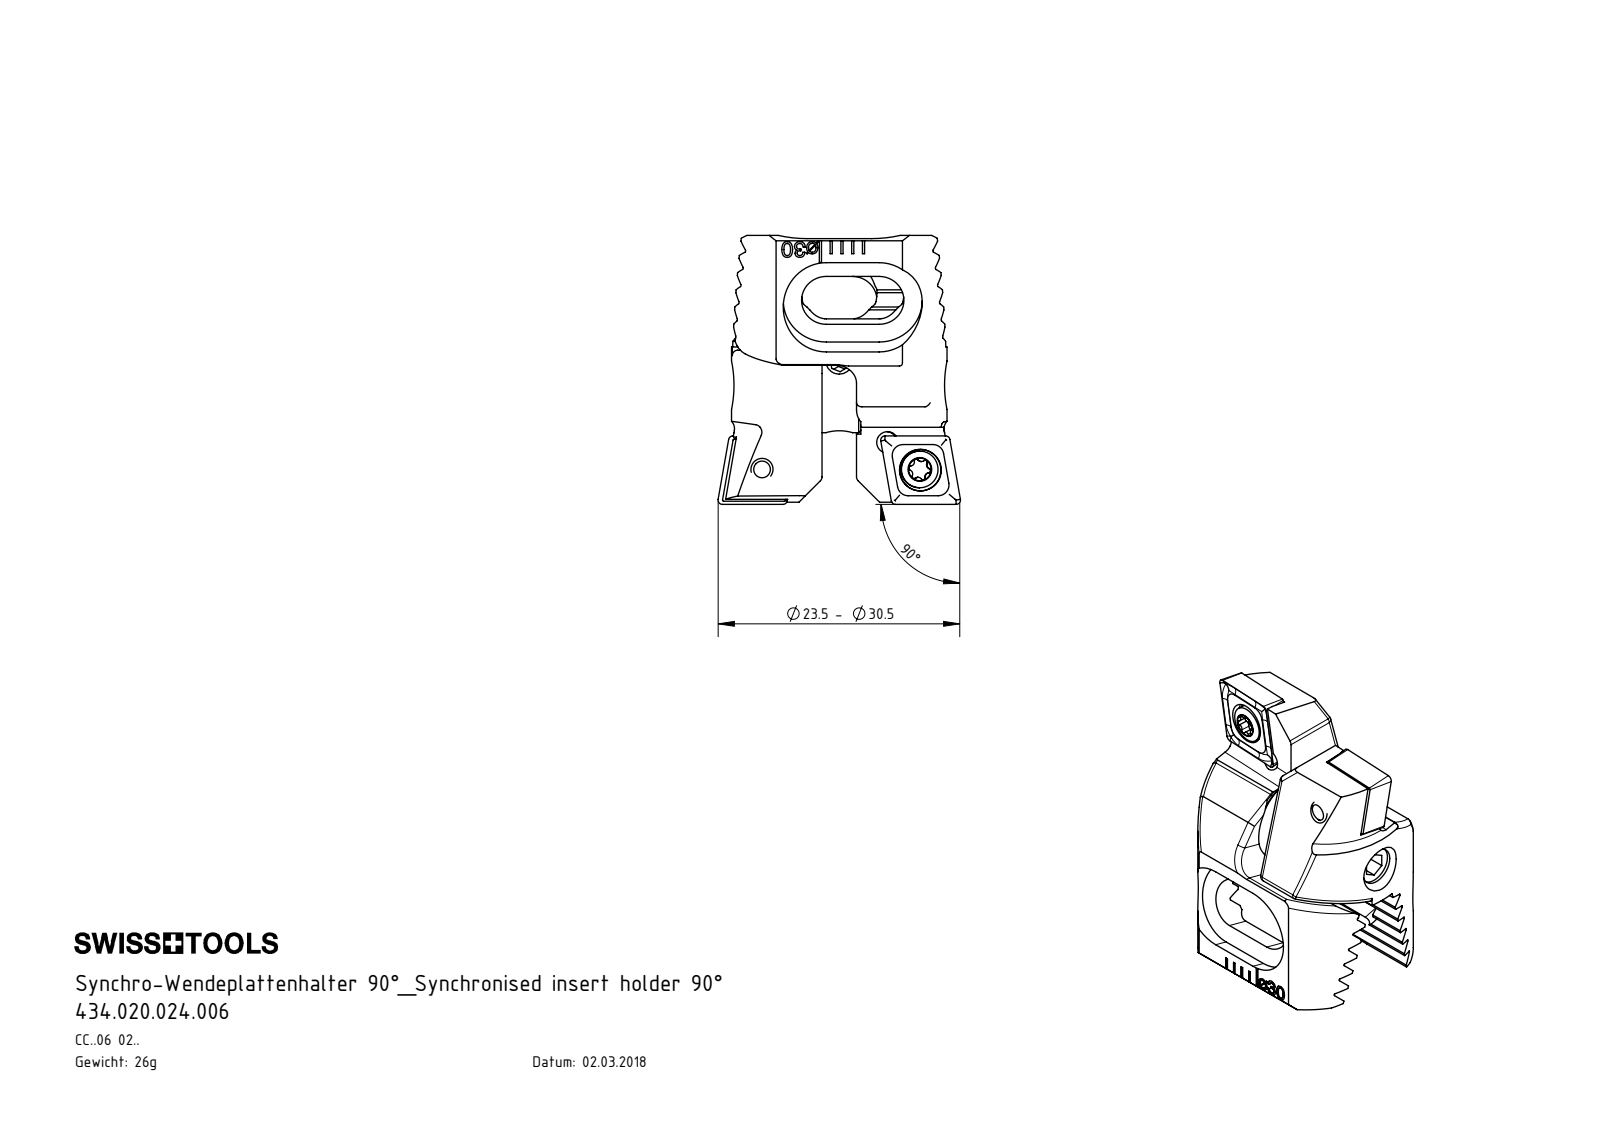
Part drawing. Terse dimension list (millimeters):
name: Z20-ER3.002.004_A; Z20-ER3.001.018_A; CCMT060204; WCA-ER2.001.006_A (+4 more)
written by: SolidWorks 2017 (CONFIG_CONTROL_DESIGN)
unit: mm
bodies: 11 solids, 485 faces (189 planar, 158 cylindrical, 138 other)
size: 24.95 × 22.42 × 16.3
volume: 3 171 mm³; area: 3 798 mm²
holes: 3× ⌀1, 3× ⌀2.5, 2× ⌀2, 2× ⌀2.05, 2× ⌀2.8, 2× ⌀3.85, 1× ⌀3.5, 1× ⌀9.1
bosses: 4× ⌀3, 2× ⌀3.4, 2× ⌀2.5, 1× ⌀8.8, 1× ⌀4
rounds: 12× R0.12, 12× R0.21, 10× R0.36, 8× R1, 4× R0.5, 4× R2.3, 4× R4, 2× R0.36
face distances: 1.43, 2.86, 4.29, 4, 5.72, 2.57, 3.85, 7.14, 5.71, 0.42
hole spacings: 3.99, 4.09, 12.02, 12.12, 14.88, 2, 5.99, 6
